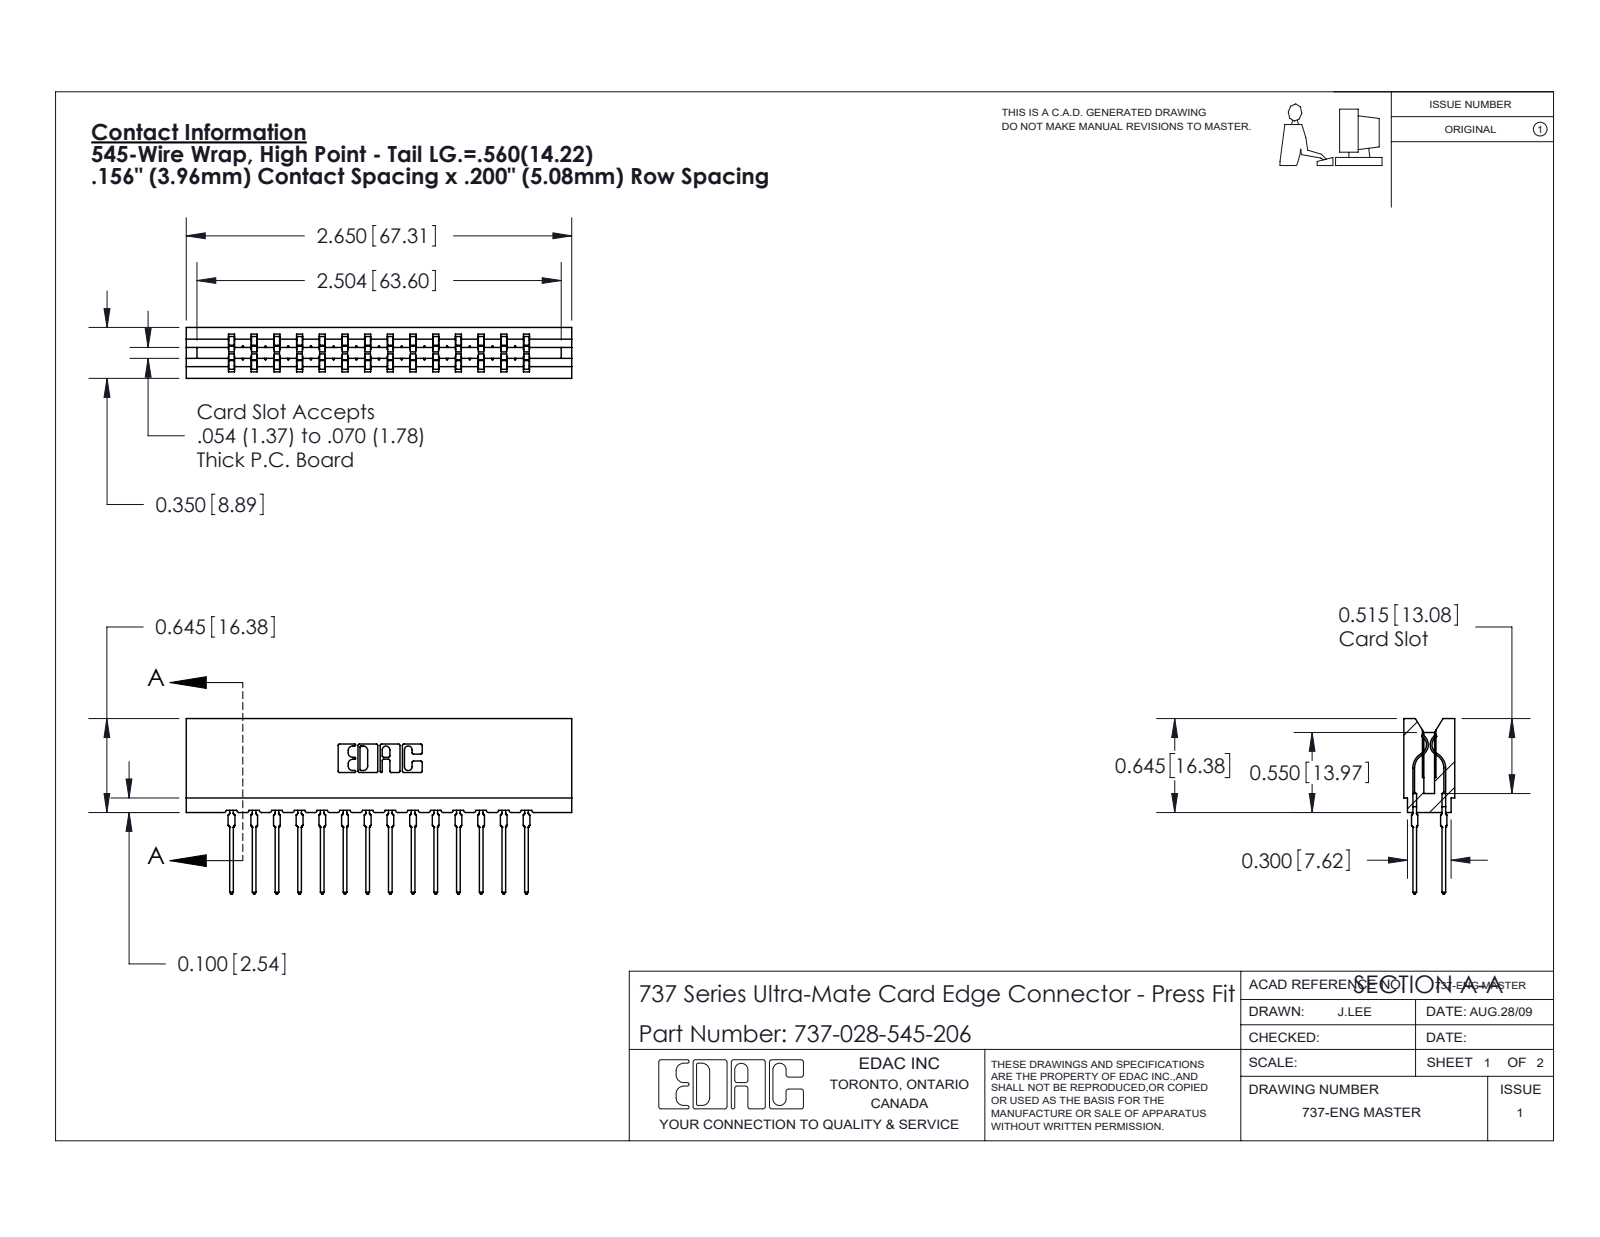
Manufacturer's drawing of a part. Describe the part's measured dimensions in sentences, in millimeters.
The part is named "745-292-001_545; 737-028-545-206; 737 Part_Insulator Option - 06". Its 3-D file was written by "SolidWorks 2020 (CONFIG_CONTROL_DESIGN)". It is 29 solids with 2615 faces: 1357 planar, 530 cylindrical and 728 other. Overall it measures 67.3 by 30.6 by 8.9 millimeters. Its volume is 6 920 cubic millimeters and its surface area 9 910 square millimeters. Partial cylindrical surfaces (rounded edges, fillets, slot ends): 56 of radius 0.5, 28 of radius 0.4, 22 of radius 0.3, 8 of radius 0.1, 8 of radius 0.3, 6 of radius 0.2, 6 of radius 0.8, 3 of radius 0.7. The main face-to-face distances are 3.5, 5.4, 8.9, 4, 15.8, 1.6, 7.3, 1.9, 3.8, 19.8.
